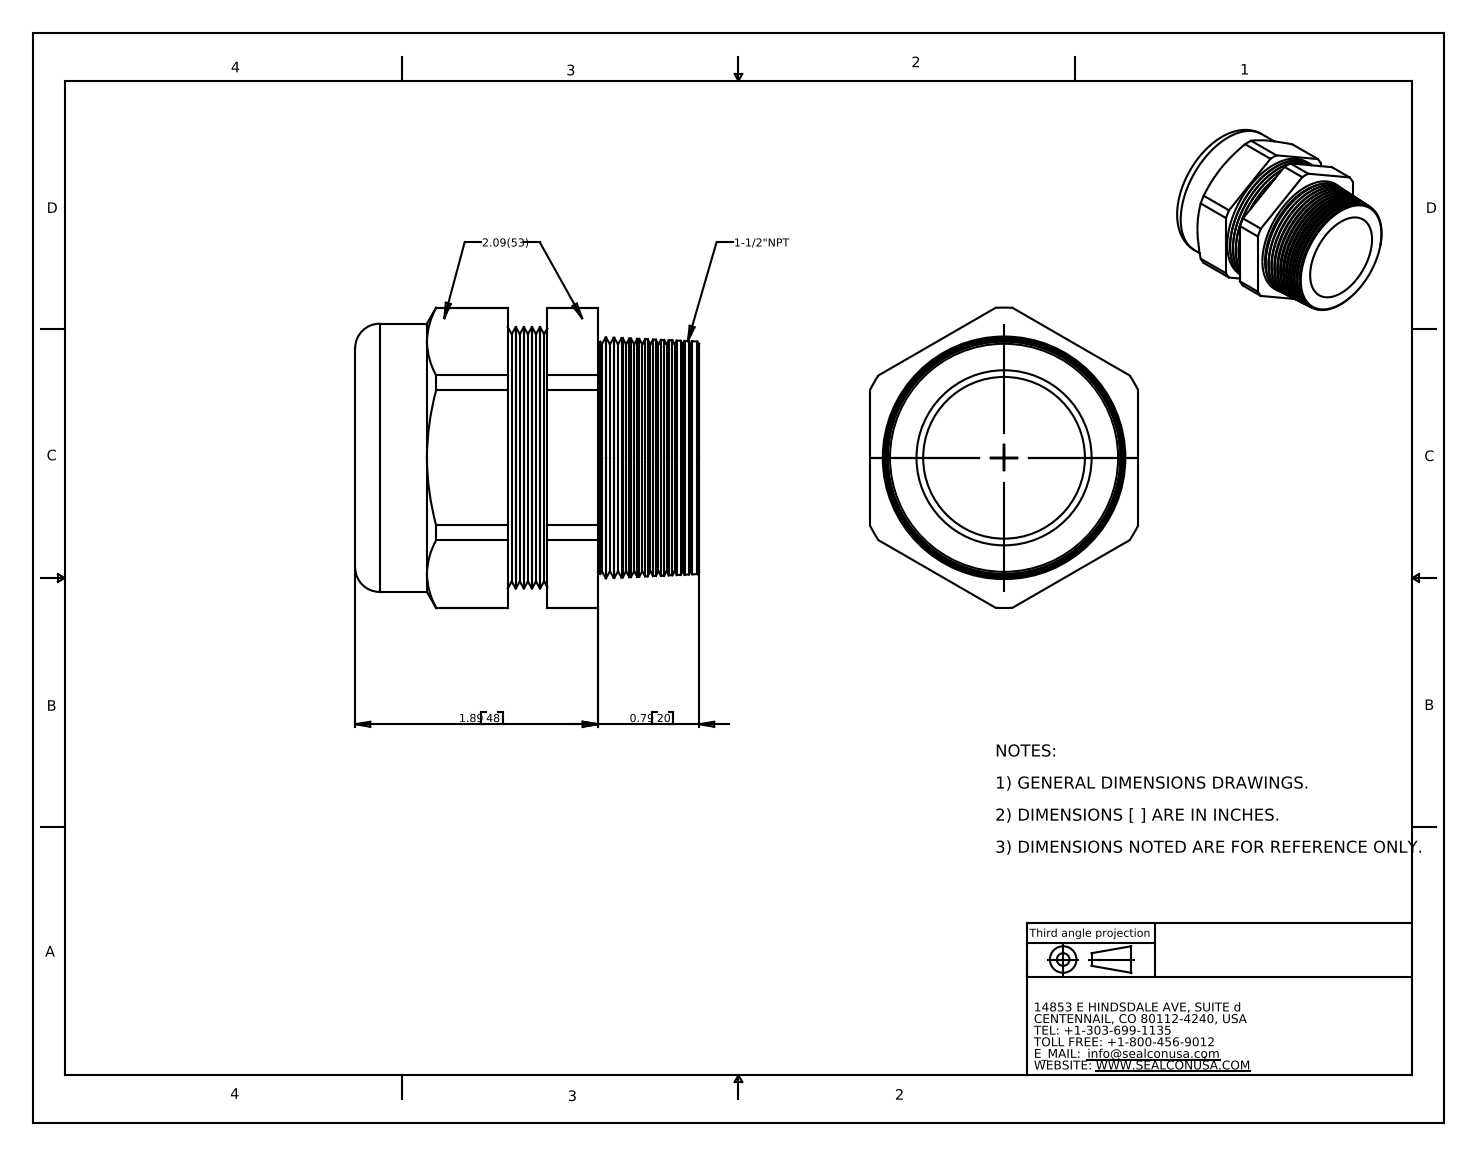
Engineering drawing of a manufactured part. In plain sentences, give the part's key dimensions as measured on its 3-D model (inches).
The part is named "CD36NR-GY". Its 3-D file was written by "SolidWorks 2007 (CONFIG_CONTROL_DESIGN)". It is 2 solids with 164 faces: 20 planar, 32 cylindrical and 112 other. Overall it measures 2.68 by 2.341 by 2.09 inches. Its volume is 6.364 cubic inches and its surface area 45.22 square inches. Round holes: 1 of diameter 1.02, 1 of diameter 1.598. Round bosses or shafts: 1 of diameter 2.09, 1 of diameter 2.035. Partial cylindrical surfaces (rounded edges, fillets, slot ends): 1 of radius 1.17. The main face-to-face distances are 2.09, 2.121, 0.539, 2.66, 1.87, 1.331, 0.79, 1.477, 0.938, 0.393.
